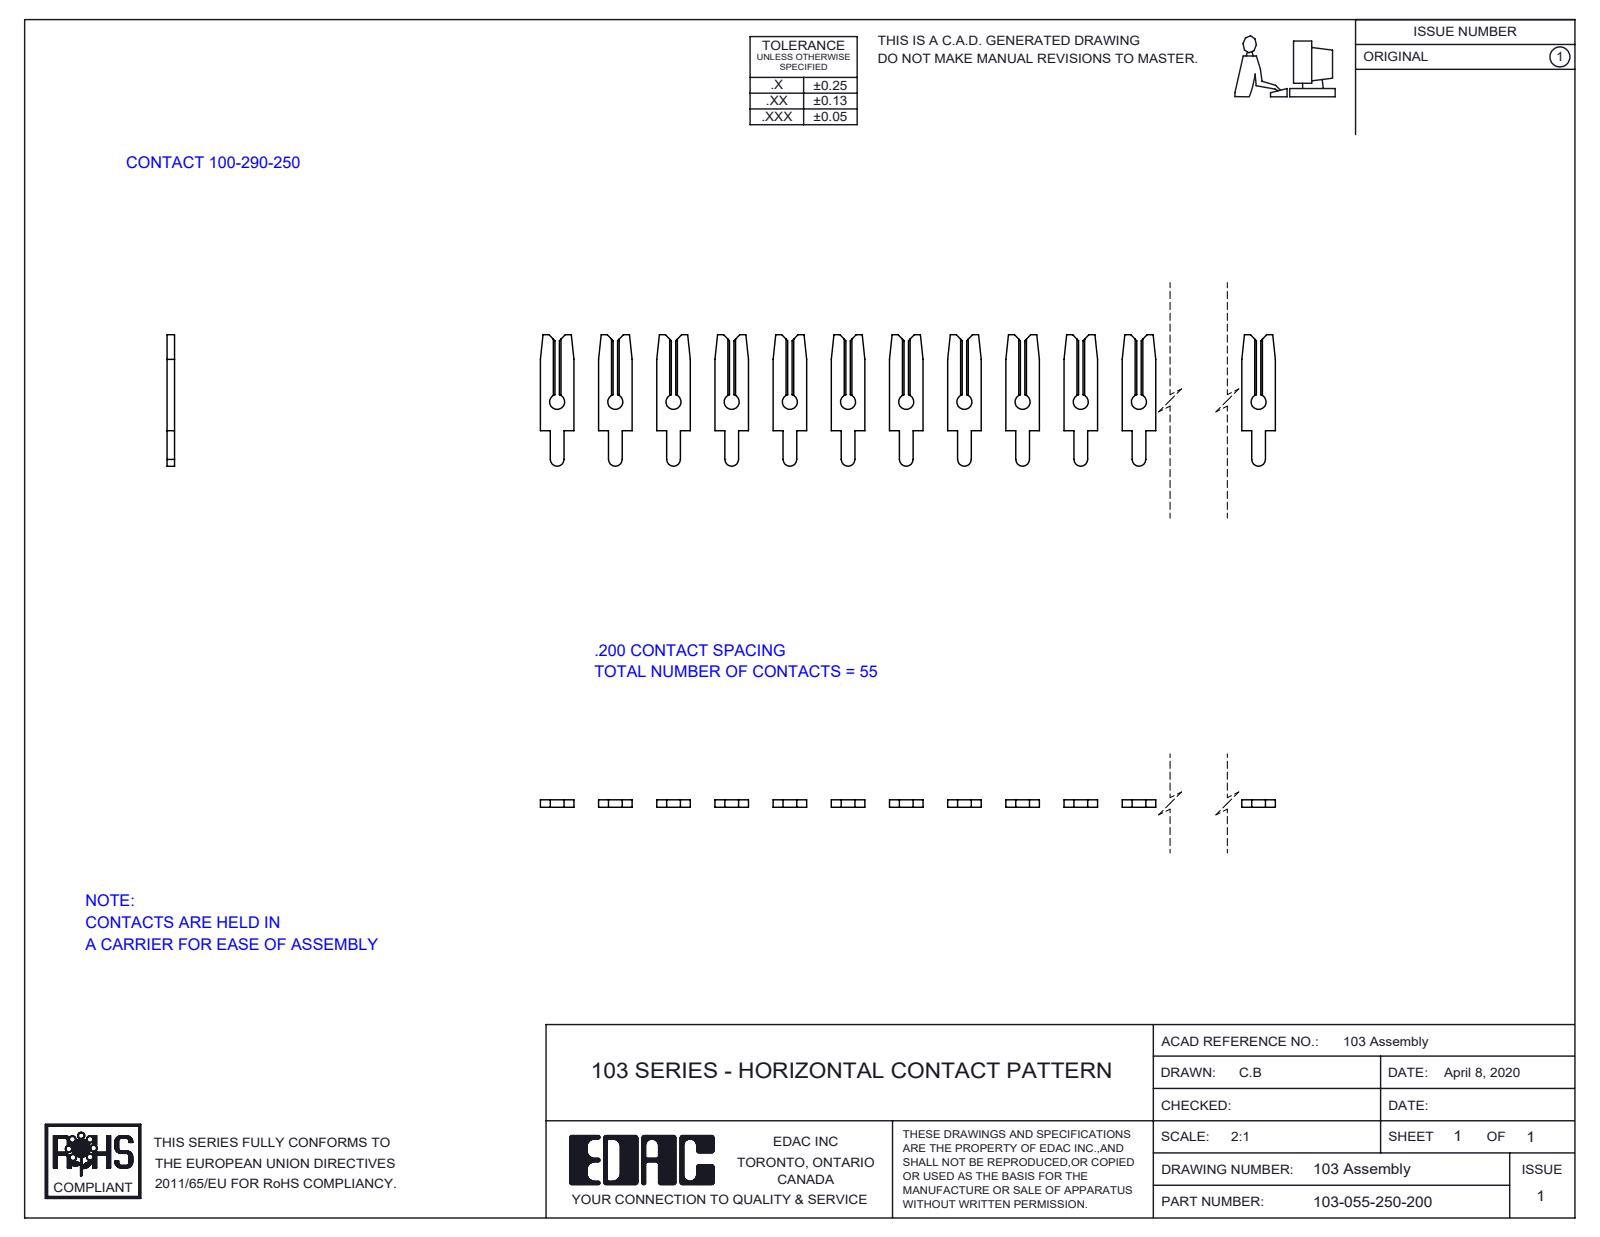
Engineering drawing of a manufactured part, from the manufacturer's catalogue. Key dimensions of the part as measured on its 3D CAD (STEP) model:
Part name (STEP PRODUCT): 103-055-250-200; 100-290-001_100-290-250
STEP written by: SolidWorks 2016 (CONFIG_CONTROL_DESIGN)
Units: inches
Bodies: 55 solids, 1320 faces (1100 planar, 220 cylindrical, 0 other)
Overall size (bounding box): 10.915 × 0.452 × 0.026
Volume: 0.052 in³ · Surface area: 6.253 in²
Round holes (diameter × count): ⌀0.052 ×55
Partial cylindrical surfaces — rounded edges, fillets, slot ends (radius × count): R0.024 ×55
Main face-to-face distances: 0.026, 0.141, 0.2, 0.4, 0.283, 0.848, 0.6, 0.99, 0.707, 0.8
Hole centre spacings: 0.2, 0.4, 0.6, 0.8, 1, 1.2, 1.4, 1.6
